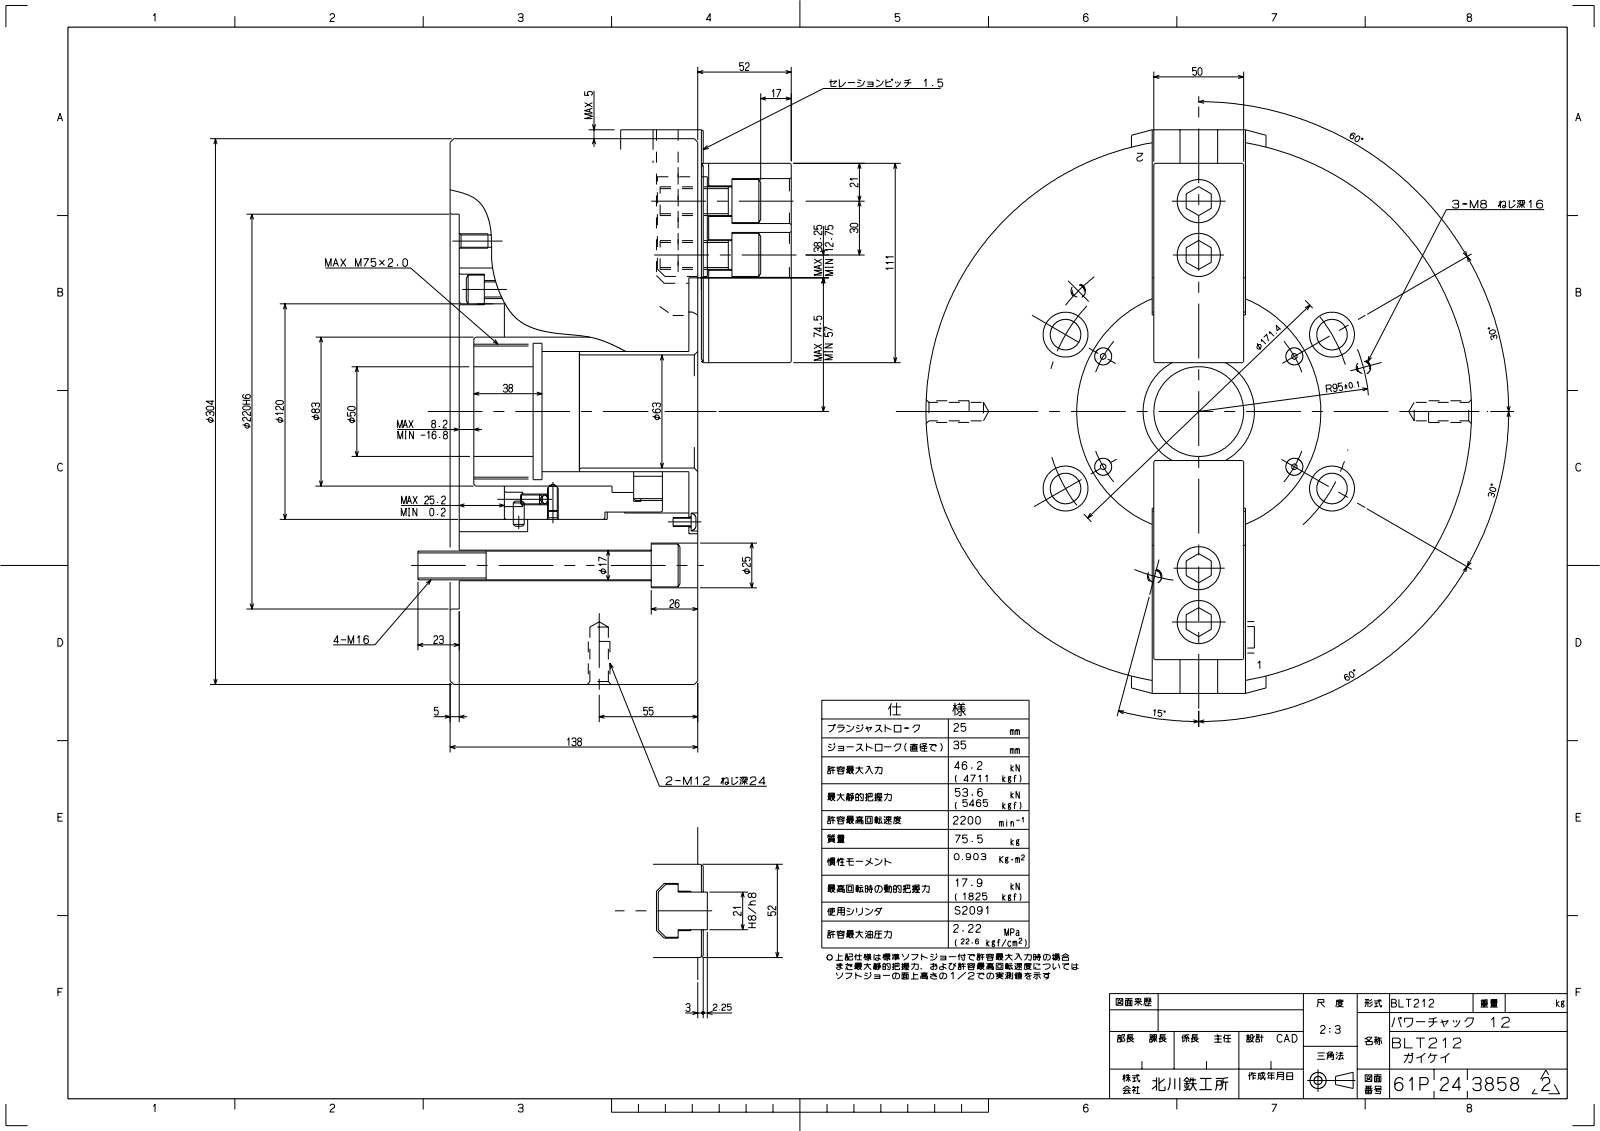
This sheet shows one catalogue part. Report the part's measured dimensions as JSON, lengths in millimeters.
{"part_name": "BL212-Solid", "step_written_by": "ST-DEVELOPER v16.7 (AUTOMOTIVE_DESIGN)", "units": "millimeters", "bodies": {"solids": 35, "faces": 3136, "planar": 2169, "cylindrical": 768, "other": 199}, "overall_size": [304.21, 304, 208.2], "volume_mm3": 9378000, "surface_area_mm2": 912152, "round_holes": [[17, 12], [10, 8], [25, 8], [3, 6], [4.2, 6], [5.5, 6], [14, 6], [5.2, 4], [8.5, 4], [6, 3], [6.8, 3], [9.5, 2]], "round_bosses_or_shafts": [[24, 8], [15.68, 8], [16, 4], [9.73, 4], [9.5, 4], [4.83, 4], [23.5, 2], [6, 2]], "partial_cylinders_radius": [[0.1, 262], [1.2, 12], [7.5, 8], [0.8, 6], [13, 6], [0.6, 4], [4, 4], [6.72, 4]], "face_to_face_distances": [5, 133, 138, 38, 1, 51, 20, 90, 128, 95], "hole_center_spacings": [61.5, 85.72, 24.22, 41.48, 46.6, 47.42, 48.17, 72.16]}
